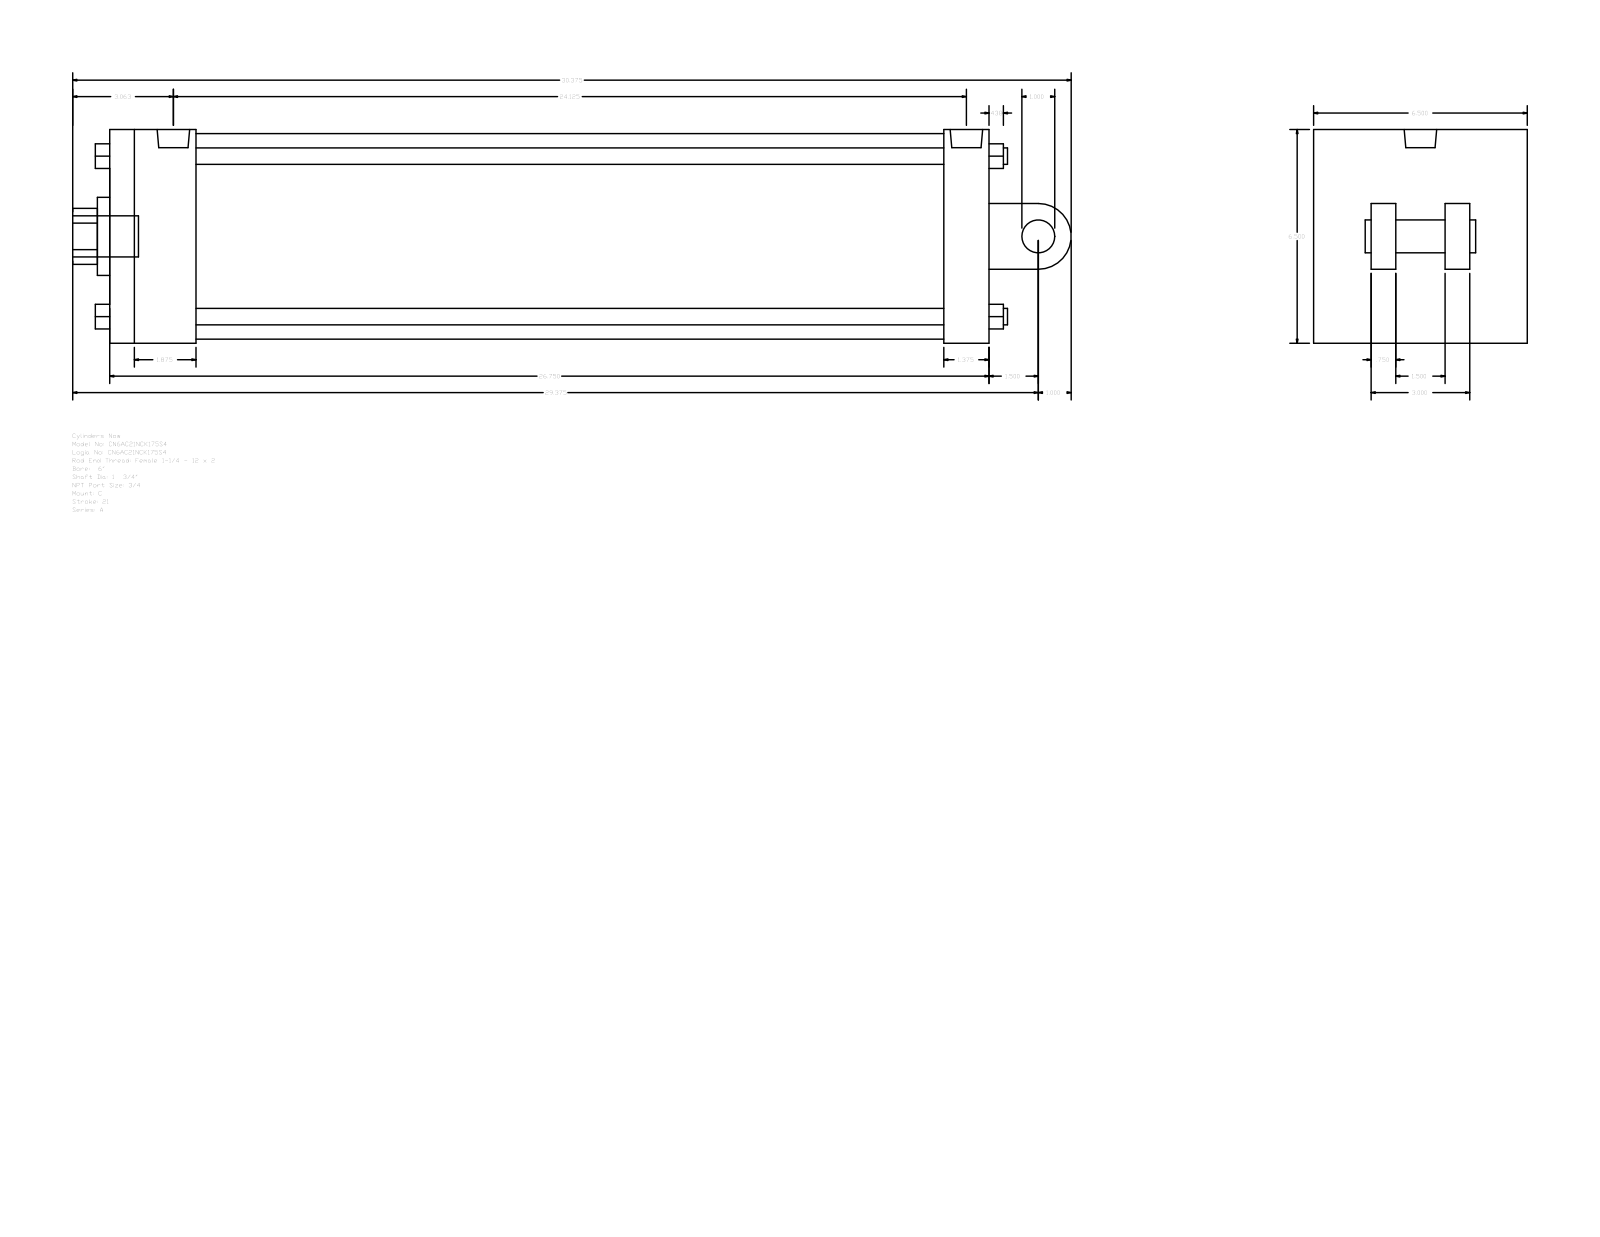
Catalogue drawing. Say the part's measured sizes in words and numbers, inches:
The part is named "A_C__0600_1.75". Its 3-D file was written by "GSSL Pune (CONFIG_CONTROL_DESIGN)". It is 0 solids with 135 faces: 102 planar, 33 cylindrical and 0 other. Overall it measures 30.375 by 6.5 by 6.5 inches. Round holes: 2 of diameter 0.594, 1 of diameter 0.989, 1 of diameter 1.75, 1 of diameter 2.375, 1 of diameter 6.25. Round bosses or shafts: 4 of diameter 0.5, 2 of diameter 0.594, 1 of diameter 1.25, 1 of diameter 1, 1 of diameter 0.989. Partial cylindrical surfaces (rounded edges, fillets, slot ends): 1 of radius 0.852, 1 of radius 1. The main face-to-face distances are 6.5, 26.75, 0.75, 2.25, 1.375, 2.625, 24.125, 25.375, 22.75, 1.75. The hole center spacings are 0.219.
